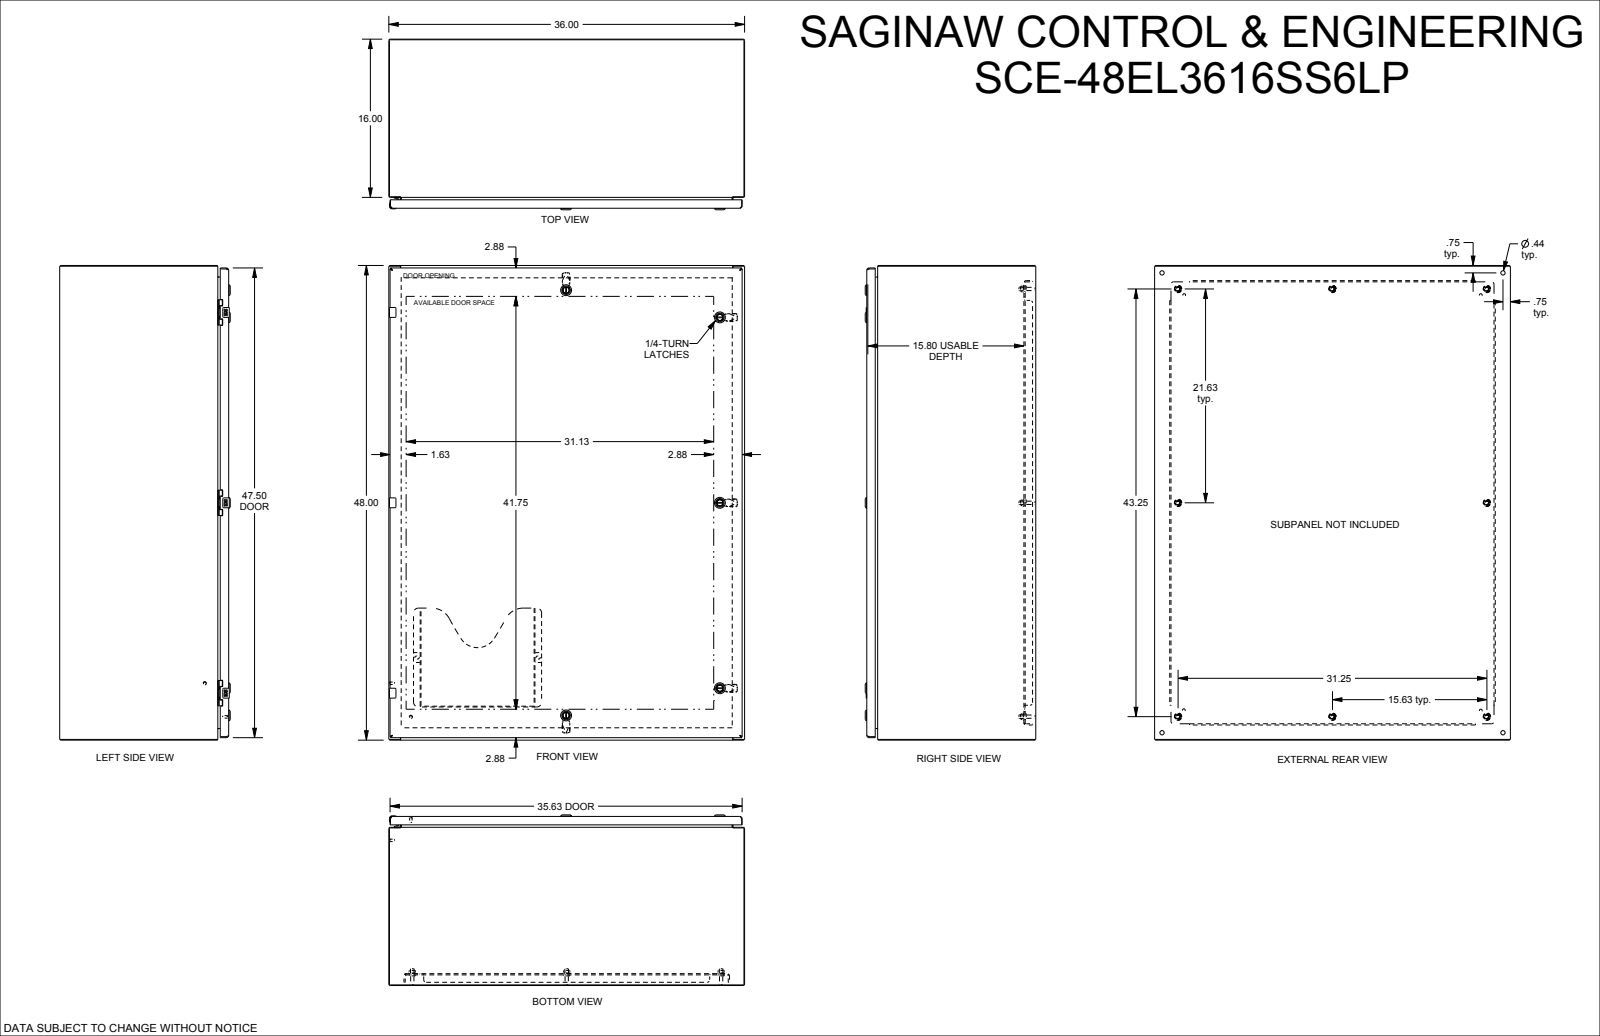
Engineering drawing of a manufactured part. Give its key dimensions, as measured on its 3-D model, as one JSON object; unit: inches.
{"part_name": "SCE-48EL3616SS6LP", "step_written_by": "SolidWorks 2019 (CONFIG_CONTROL_DESIGN)", "units": "inches", "bodies": {"solids": 0, "faces": 4752, "planar": 2321, "cylindrical": 1312, "other": 1119}, "overall_size": [48, 36, 17.256], "round_holes": [[0.367, 8], [0.5, 8], [0.172, 6], [0.205, 6], [0.244, 6], [0.266, 6], [0.197, 5], [0.315, 5], [0.394, 5], [0.634, 5], [0.281, 4], [0.375, 4]], "round_bosses_or_shafts": [[0.17, 9], [0.366, 8], [0.332, 8], [0.25, 6], [1.102, 5], [0.866, 5], [0.802, 5], [0.78, 5]], "partial_cylinders_radius": [[0.012, 142], [0.01, 52], [0.02, 52], [0.015, 36], [0.04, 23], [0.157, 20], [0.07, 14], [0.03, 13]], "face_to_face_distances": [0.075, 0.104, 16.995, 16.92, 17.099, 17.024, 0.075, 1.125, 15.795, 35.925], "hole_center_spacings": [19.25, 38.5, 0.049, 0.986, 18.265, 19.25, 19.25, 20.235]}
